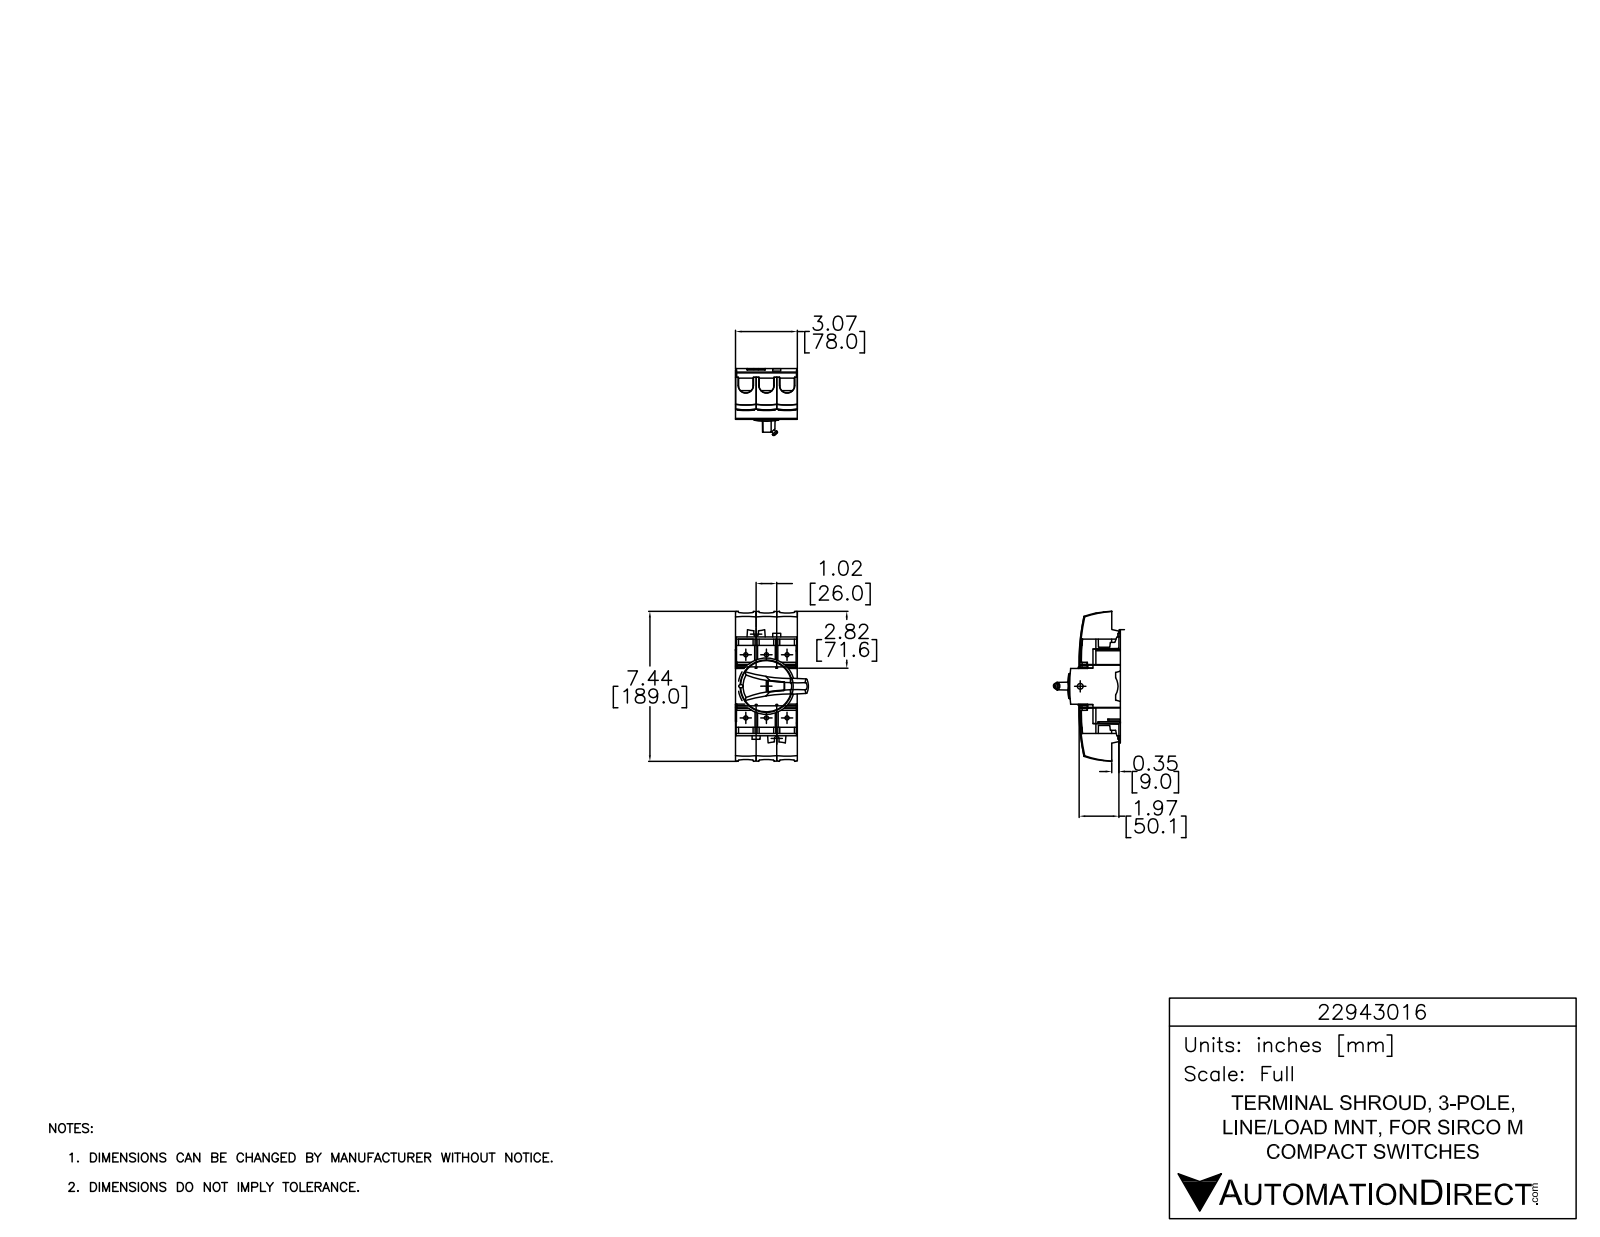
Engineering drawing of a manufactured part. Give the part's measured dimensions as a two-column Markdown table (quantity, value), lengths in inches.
| quantity | value |
| --- | --- |
| part name | 22943016 |
| STEP written by | SolidWorks 2015 (AUTOMOTIVE_DESIGN) |
| units | inches |
| bodies | 1 solid, 102 faces (73 planar, 9 cylindrical, 20 other) |
| overall size | 3.071 × 2.82 × 1.97 |
| volume | 1.267 in³ |
| surface area | 46.41 in² |
| partial cylindrical surfaces (radius × count) | 0.374 × 3, 3.547 × 3 |
| main face-to-face distances | 1.024, 2.047, 3.071, 0.937, 0.014, 0.951, 1.067, 2.004, 0.98, 2.091 |
